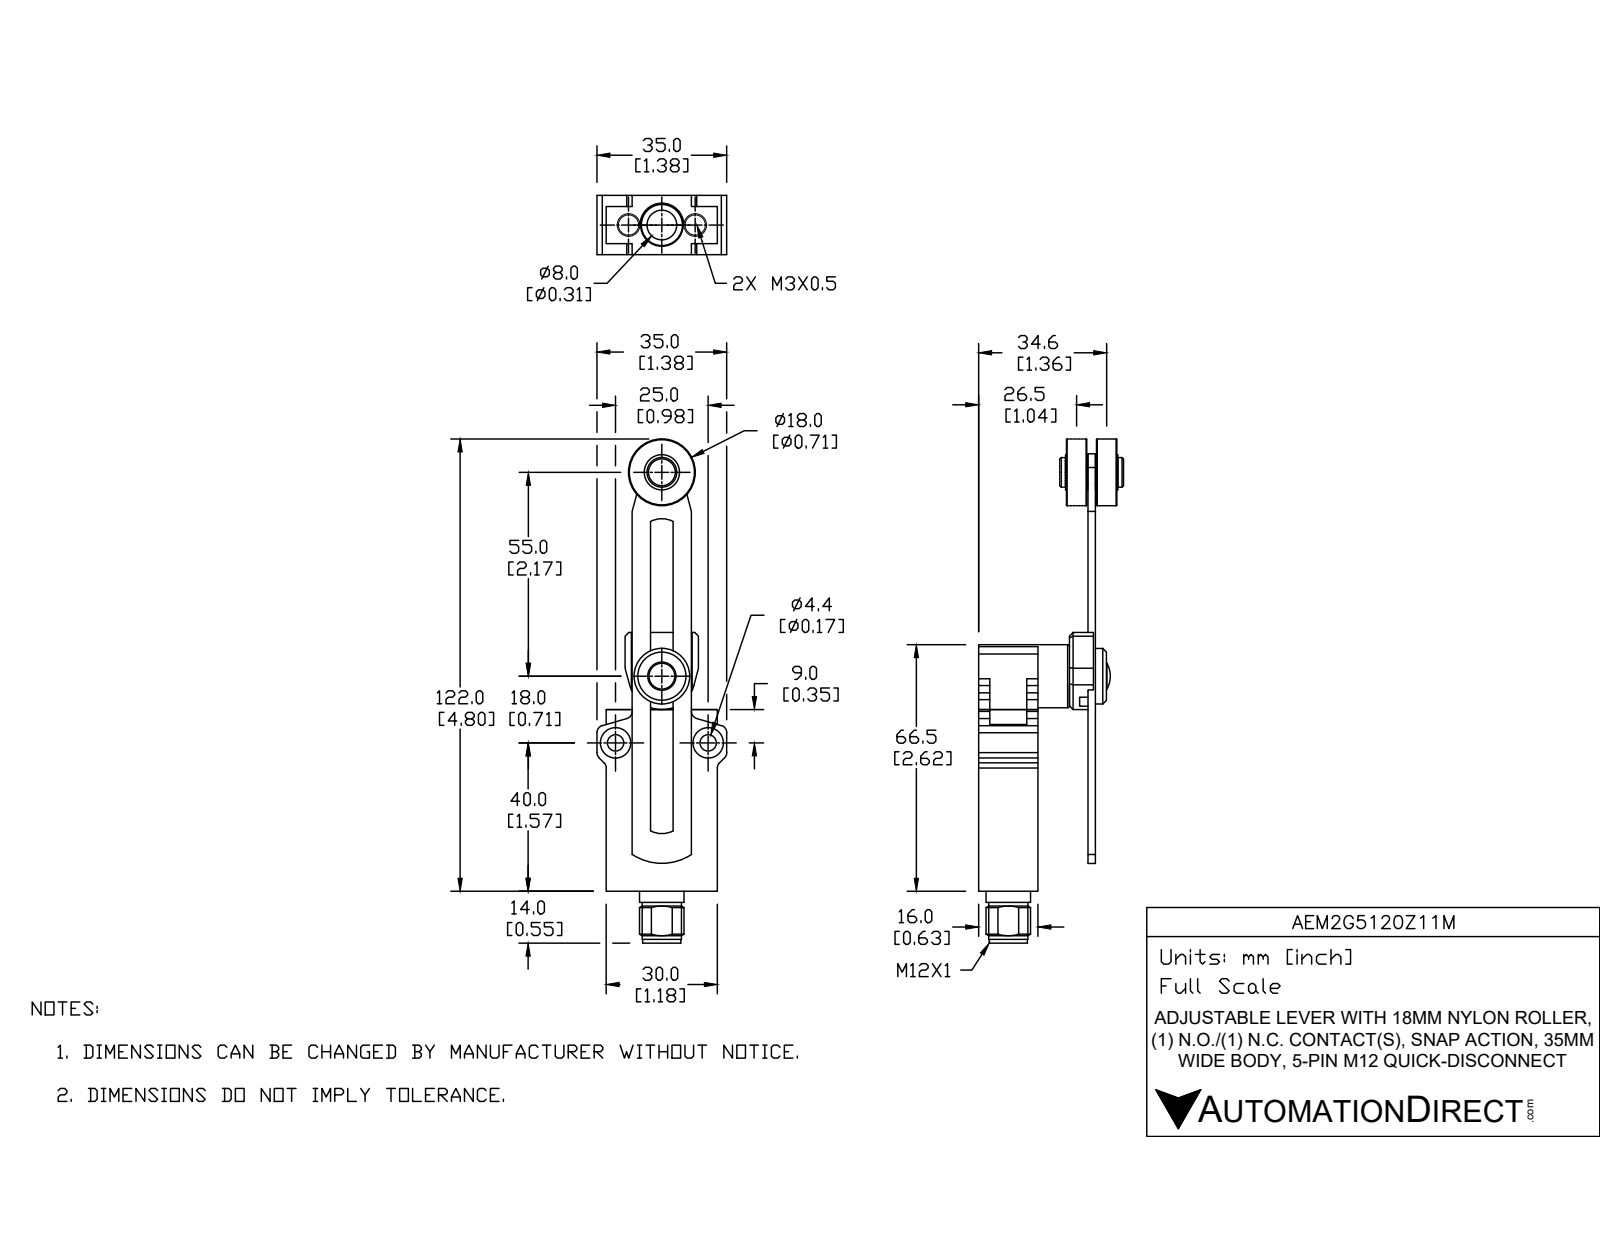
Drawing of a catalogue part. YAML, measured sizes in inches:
part_name: "AEM2G5120Z11M"
step_written_by: "SolidWorks 2018 (AUTOMOTIVE_DESIGN)"
units: inches
bodies: {solids: 8, faces: 416, planar: 195, cylindrical: 152, other: 69}
overall_size: [5.268, 1.587, 1.378]
volume: 2.146
surface_area: 24.63
round_holes:
  - {diameter: 0.118, count: 2}
  - {diameter: 0.161, count: 2}
  - {diameter: 0.173, count: 2}
  - {diameter: 0.323, count: 2}
  - {diameter: 0.098, count: 1}
  - {diameter: 0.197, count: 1}
  - {diameter: 0.224, count: 1}
  - {diameter: 0.24, count: 1}
  - {diameter: 0.299, count: 1}
round_bosses_or_shafts:
  - {diameter: 0.709, count: 1}
  - {diameter: 0.622, count: 1}
  - {diameter: 0.591, count: 1}
  - {diameter: 0.472, count: 1}
  - {diameter: 0.417, count: 1}
  - {diameter: 0.406, count: 1}
  - {diameter: 0.394, count: 1}
  - {diameter: 0.276, count: 1}
partial_cylinders:
  - {radius: 0.006, count: 36}
  - {radius: 0.079, count: 10}
  - {radius: 0.008, count: 4}
  - {radius: 0.047, count: 4}
  - {radius: 0.039, count: 3}
  - {radius: 0.256, count: 3}
  - {radius: 0.031, count: 2}
  - {radius: 0.059, count: 1}
face_to_face_distances: [0.63, 1.291, 0.661, 1.181, 0.047, 0.614, 1.244, 0.28, 0.902, 2.047]
hole_center_spacings: [0.863, 0.748, 0.984, 1.961, 2.713, 2.715]
